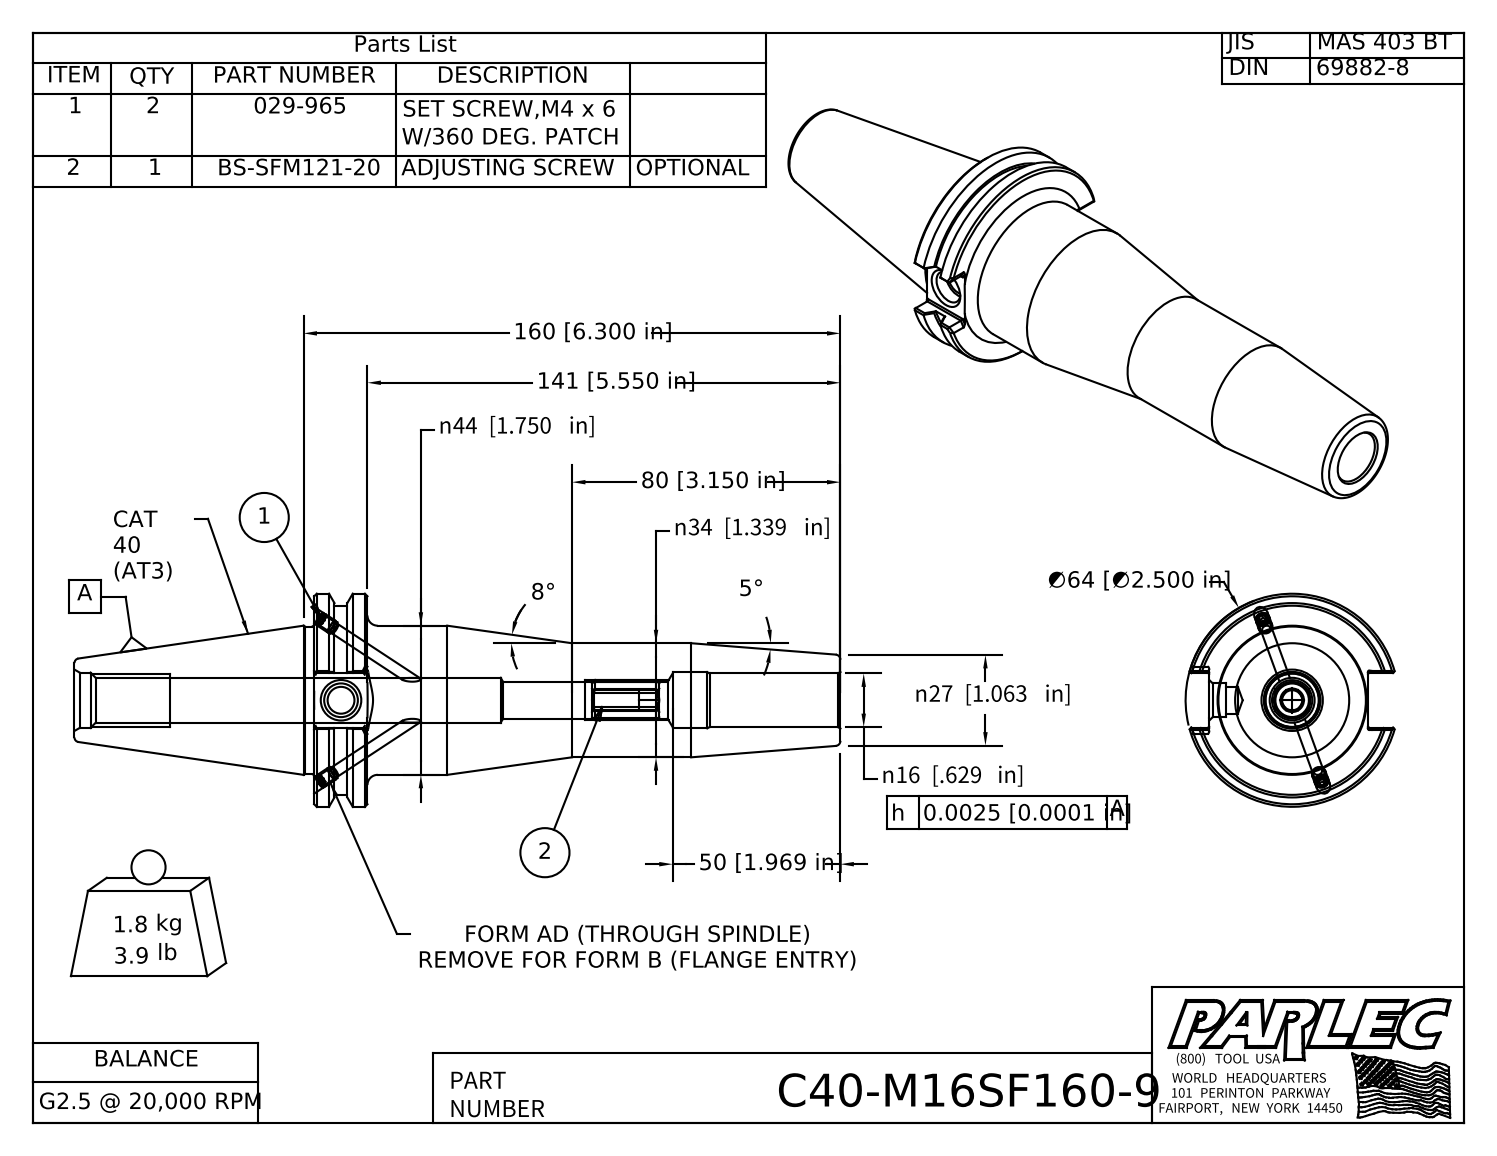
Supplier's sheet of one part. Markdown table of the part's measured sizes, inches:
| quantity | value |
| --- | --- |
| part name | C40-M16SF160-9; C40BC-M16SF160-9-1; 029-965; BS-SFM121-20 |
| STEP written by | Autodesk Inventor 2009 (AUTOMOTIVE_DESIGN) |
| units | inches |
| bodies | 4 solids, 153 faces (66 planar, 35 cylindrical, 52 other) |
| overall size | 8.987 × 2.5 × 2.406 |
| volume | 13.9 in³ |
| surface area | 66.9 in² |
| round holes (diameter × count) | 0.13 × 2, 0.161 × 2, 0.629 × 1, 0.659 × 1 |
| round bosses / shafts (diameter × count) | 0.165 × 2, 0.157 × 2, 2.5 × 1, 2.219 × 1, 1.75 × 1, 1.73 × 1, 1.339 × 1 |
| partial cylindrical surfaces (radius × count) | 0.02 × 12, 0.236 × 1 |
| main face-to-face distances | 0.625, 6.175, 5.55, 0.236, 0.64, 0.394, 1.86, 0.691, 1.169, 1.085 |
